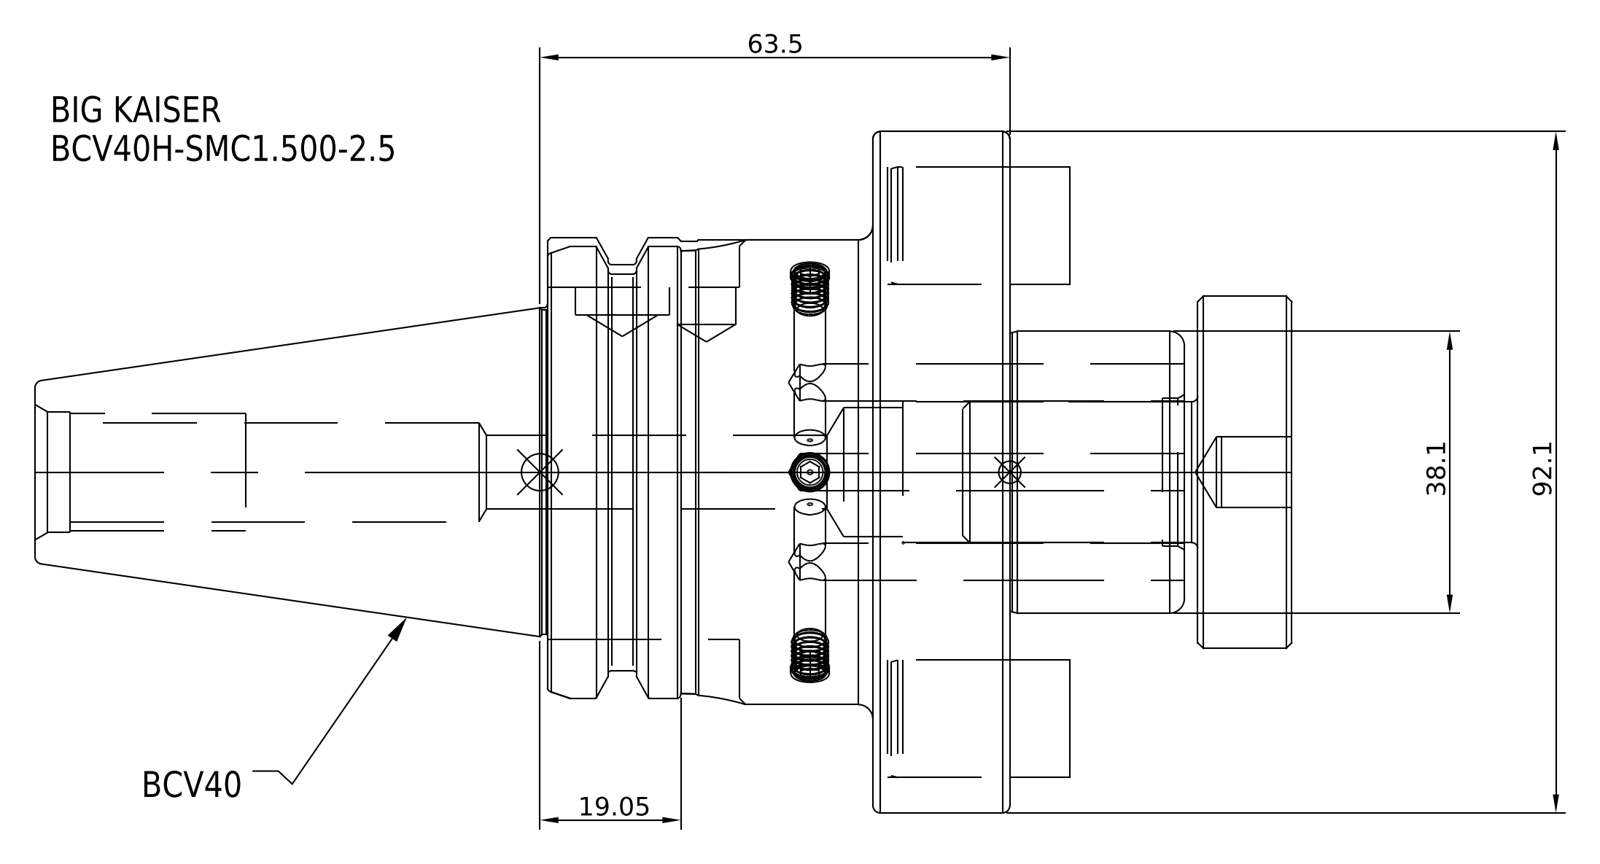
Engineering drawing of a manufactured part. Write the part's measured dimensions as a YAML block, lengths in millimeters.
part_name: "BCV40H-SMC1_500-2_5"
step_written_by: "SolidWorks 2021 (CONFIG_CONTROL_DESIGN)"
units: millimeters
bodies: {solids: 1, faces: 43, planar: 17, cylindrical: 16, other: 10}
overall_size: [139.83, 92.1, 92.1]
volume: 324055
surface_area: 36881
round_holes:
  - {diameter: 17.46, count: 1}
round_bosses_or_shafts:
  - {diameter: 92.1, count: 1}
  - {diameter: 63.5, count: 1}
  - {diameter: 62.8, count: 1}
  - {diameter: 62.4, count: 1}
  - {diameter: 56.36, count: 1}
  - {diameter: 44.45, count: 1}
face_to_face_distances: [18.5, 62.5, 44, 8.08, 26.58, 70.58, 139.83, 131.75, 113.25, 69.25]
